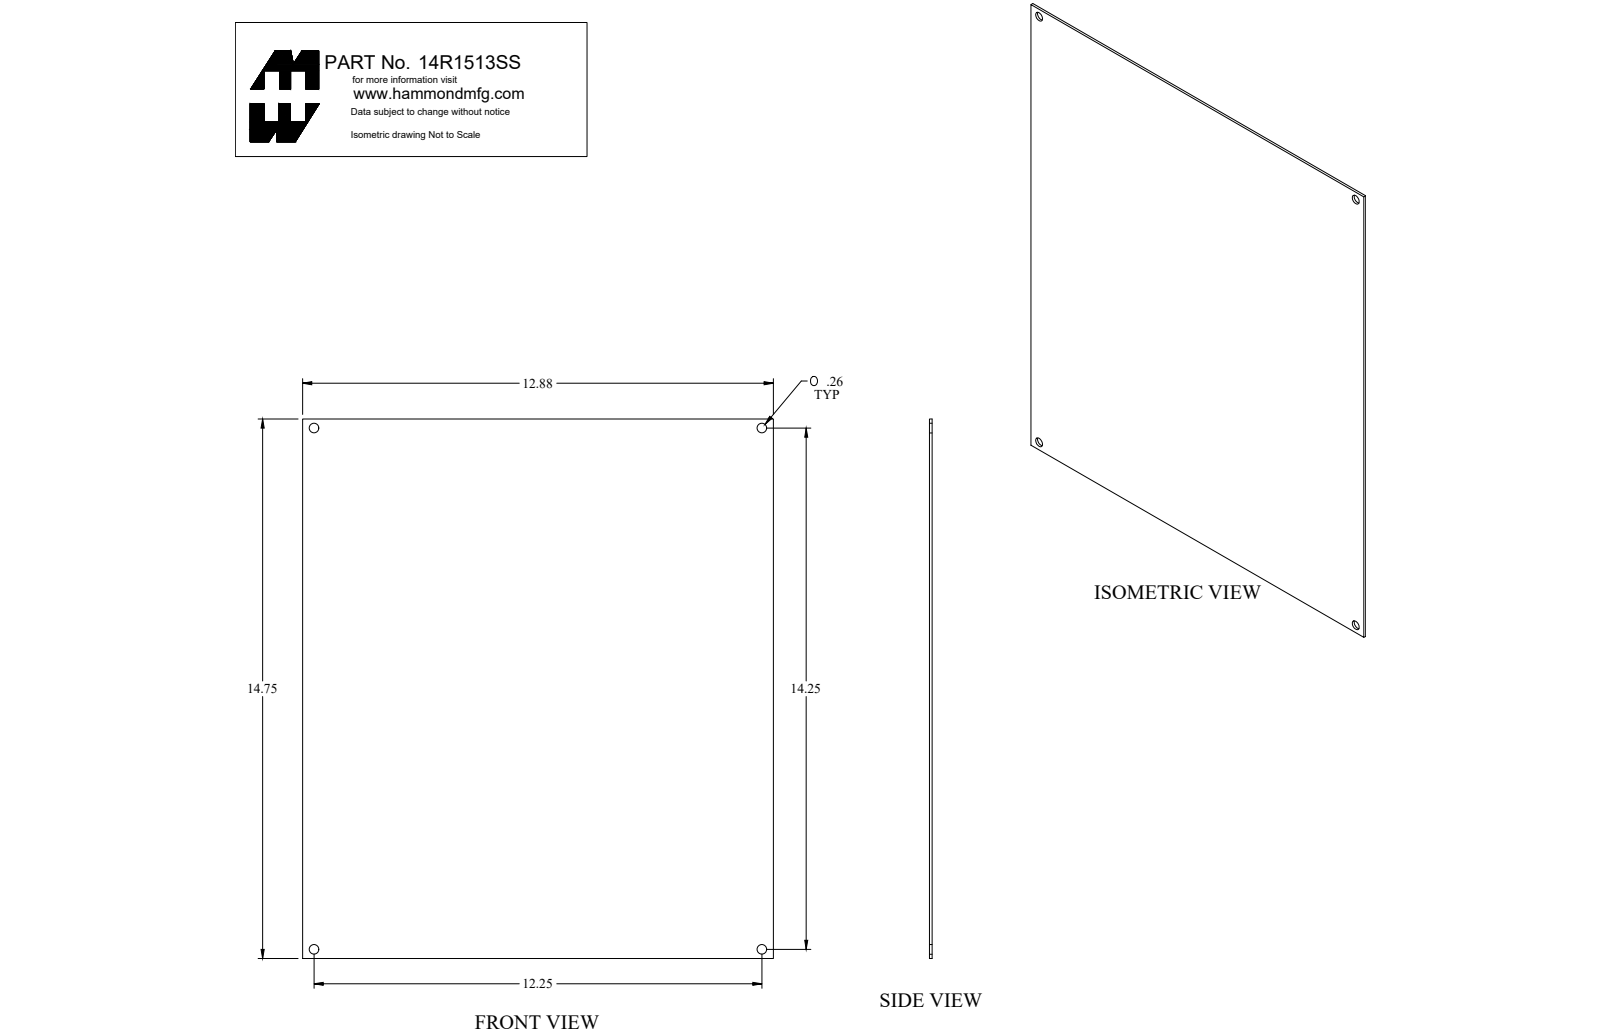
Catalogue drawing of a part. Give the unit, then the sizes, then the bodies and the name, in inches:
Units: inches
Overall size (bounding box): 14.75 × 12.875 × 0.072
Round holes (diameter × count): ⌀0.265 ×4
Main face-to-face distances: 0.072, 12.875, 14.75
Hole centre spacings: 12.25, 14.25, 18.791
Volume: 13.66 in³ · Surface area: 383.6 in²
Bodies: 1 solid, 10 faces (6 planar, 4 cylindrical, 0 other)
Part name (STEP PRODUCT): 14R1513SS
STEP written by: SolidWorks 2018 (AUTOMOTIVE_DESIGN)
